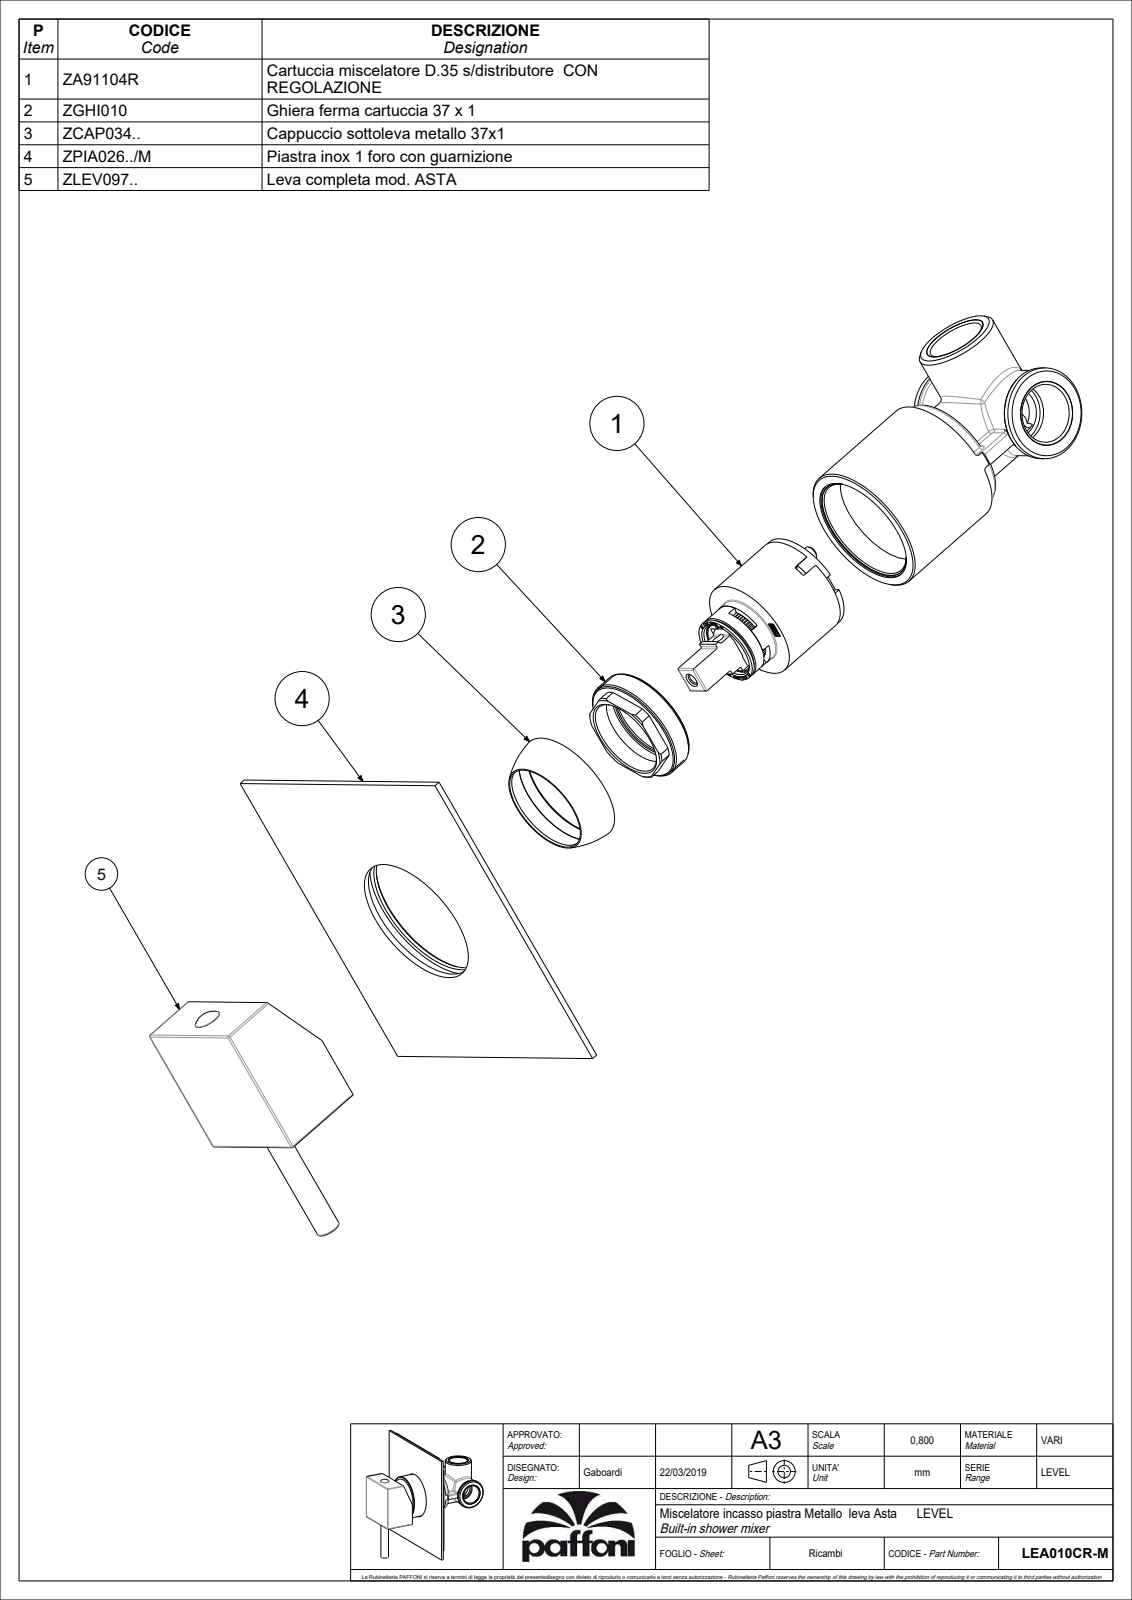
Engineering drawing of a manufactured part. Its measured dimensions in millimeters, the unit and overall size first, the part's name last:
Units: millimetres
Overall size (bounding box): 117.5 × 110 × 48.6
Round holes (diameter × count): ⌀4 ×2, ⌀3.3 ×1, ⌀5 ×1, ⌀5.5 ×1, ⌀6 ×1, ⌀8.1 ×1, ⌀19.5 ×1, ⌀19.9 ×1, ⌀26.8 ×1, ⌀29 ×1, ⌀31 ×1, ⌀32.4 ×1
Round bosses / shafts (diameter × count): ⌀44.8 ×1, ⌀35 ×1, ⌀23.5 ×1, ⌀23.4 ×1, ⌀21.8 ×1, ⌀8 ×1, ⌀5 ×1
Partial cylindrical surfaces — rounded edges, fillets, slot ends (radius × count): R0.5 ×16, R0.15 ×11, R0.3 ×4, R1 ×2, R7 ×1, R9.3 ×1, R10.85 ×1, R11.25 ×1
Main face-to-face distances: 2, 45, 48.6, 46.6, 3, 45.6, 43.6, 1.5, 9, 27
Hole centre spacings: 14.6
Volume: 59 613 mm³ · Surface area: 55 109 mm²
Bodies: 2 solids, 866 faces (571 planar, 178 cylindrical, 117 other)
Part name (STEP PRODUCT): LEA010CR-M
STEP written by: CREO PARAMETRIC BY PTC INC, 2020044 (CONFIG_CONTROL_DESIGN)
